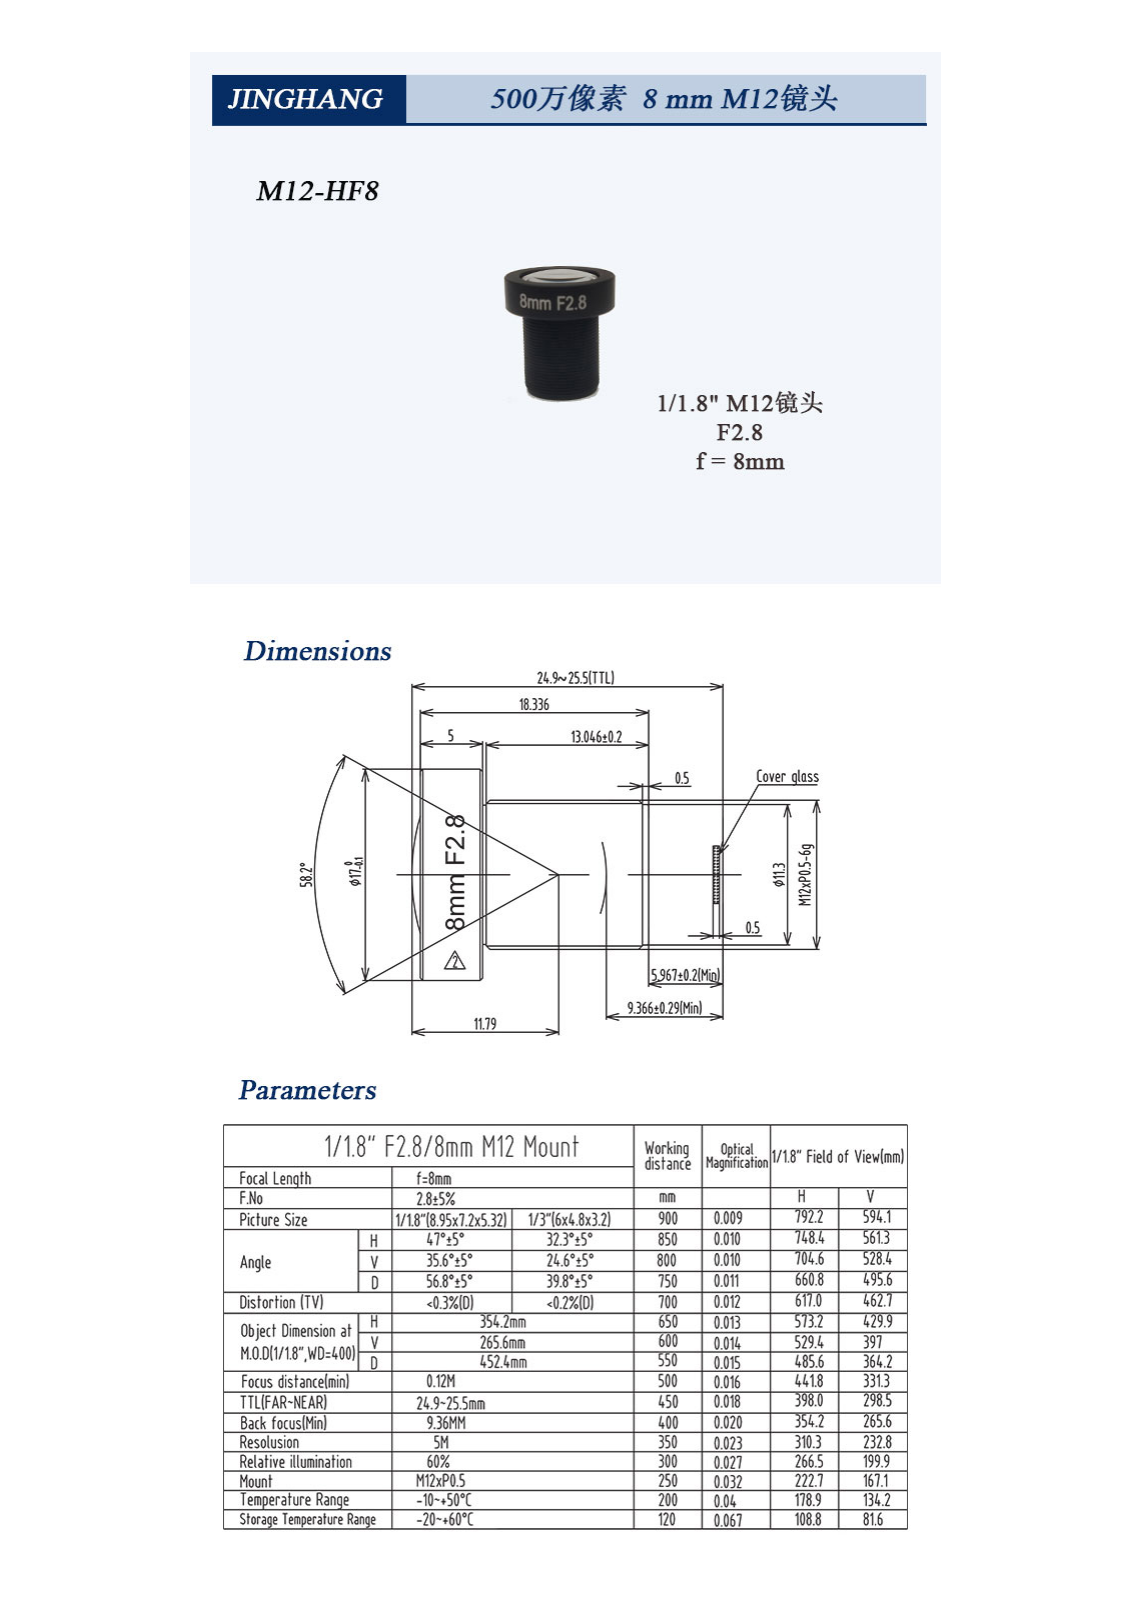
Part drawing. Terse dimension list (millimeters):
name: FS0805A-200
written by: PRO/ENGINEER BY PARAMETRIC TECHNOLOGY CORPORATION, 2010370 (CONFIG_CONTROL_DESIGN)
unit: mm
bodies: 1 solid, 115 faces (8 planar, 62 cylindrical, 45 other)
size: 19.01 × 17 × 17
volume: 2 506 mm³; area: 1 594 mm²
holes: 1× ⌀10, 1× ⌀12.2, 1× ⌀15.2
bosses: 1× ⌀17, 1× ⌀15, 1× ⌀12, 1× ⌀11.3, 1× ⌀11.2
face distances: 18.13, 4.48, 13.65, 5, 0.52, 13.13, 18.33, 13.85, 13.33, 5.28
